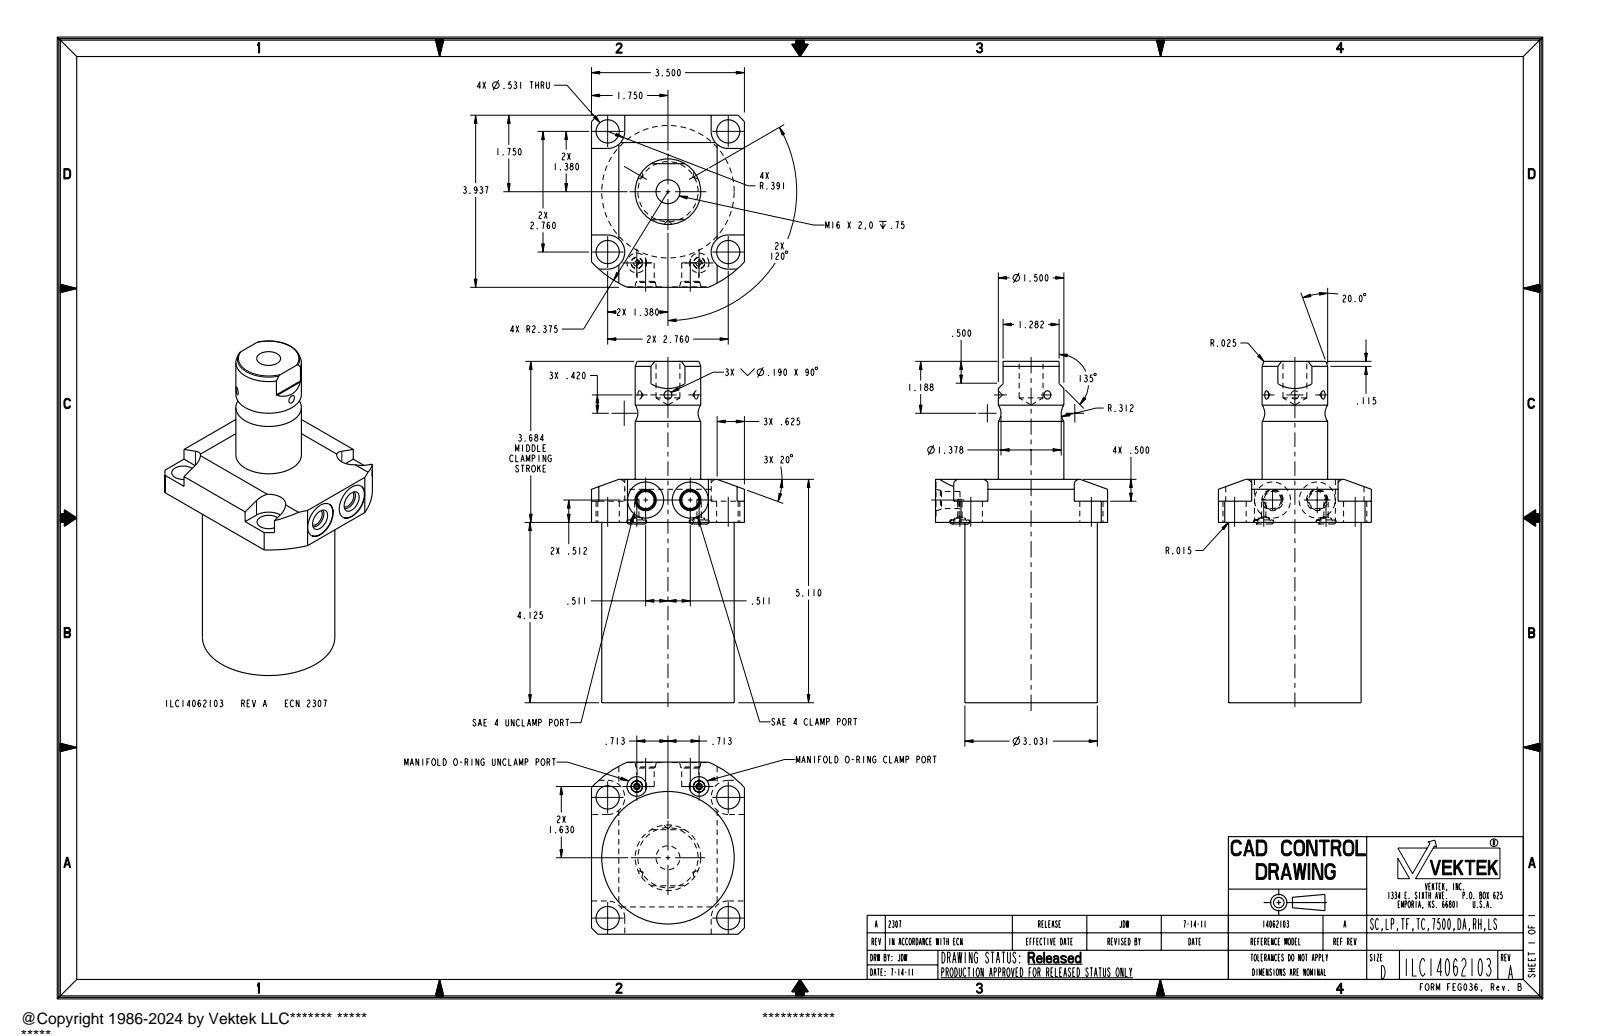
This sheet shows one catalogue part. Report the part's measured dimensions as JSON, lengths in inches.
{"part_name": "ILC14062103", "step_written_by": "PRO/ENGINEER BY PARAMETRIC TECHNOLOGY CORPORATION, 2007460 (AUTOMOTIVE_DESIGN_CC2)", "units": "inches", "bodies": {"solids": 3, "faces": 121, "planar": 39, "cylindrical": 46, "other": 36}, "overall_size": [7.809, 3.937, 3.5], "volume_in3": 45.25, "surface_area_in2": 96.73, "round_holes": [[0.531, 4], [0.098, 2], [0.256, 2], [0.392, 2], [0.449, 2], [0.825, 2], [0.546, 1]], "round_bosses_or_shafts": [[3.031, 1], [1.5, 1]], "partial_cylinders_radius": [[0.391, 4], [0.03, 2], [2.375, 1]], "face_to_face_distances": [5.11, 4.125, 0.985, 3.5, 7.809, 3.684, 2.699, 4.61, 0.485, 0.5], "hole_center_spacings": [1.952, 2.76, 0.712, 1.779, 2.108, 3.083, 3.666, 3.903]}
